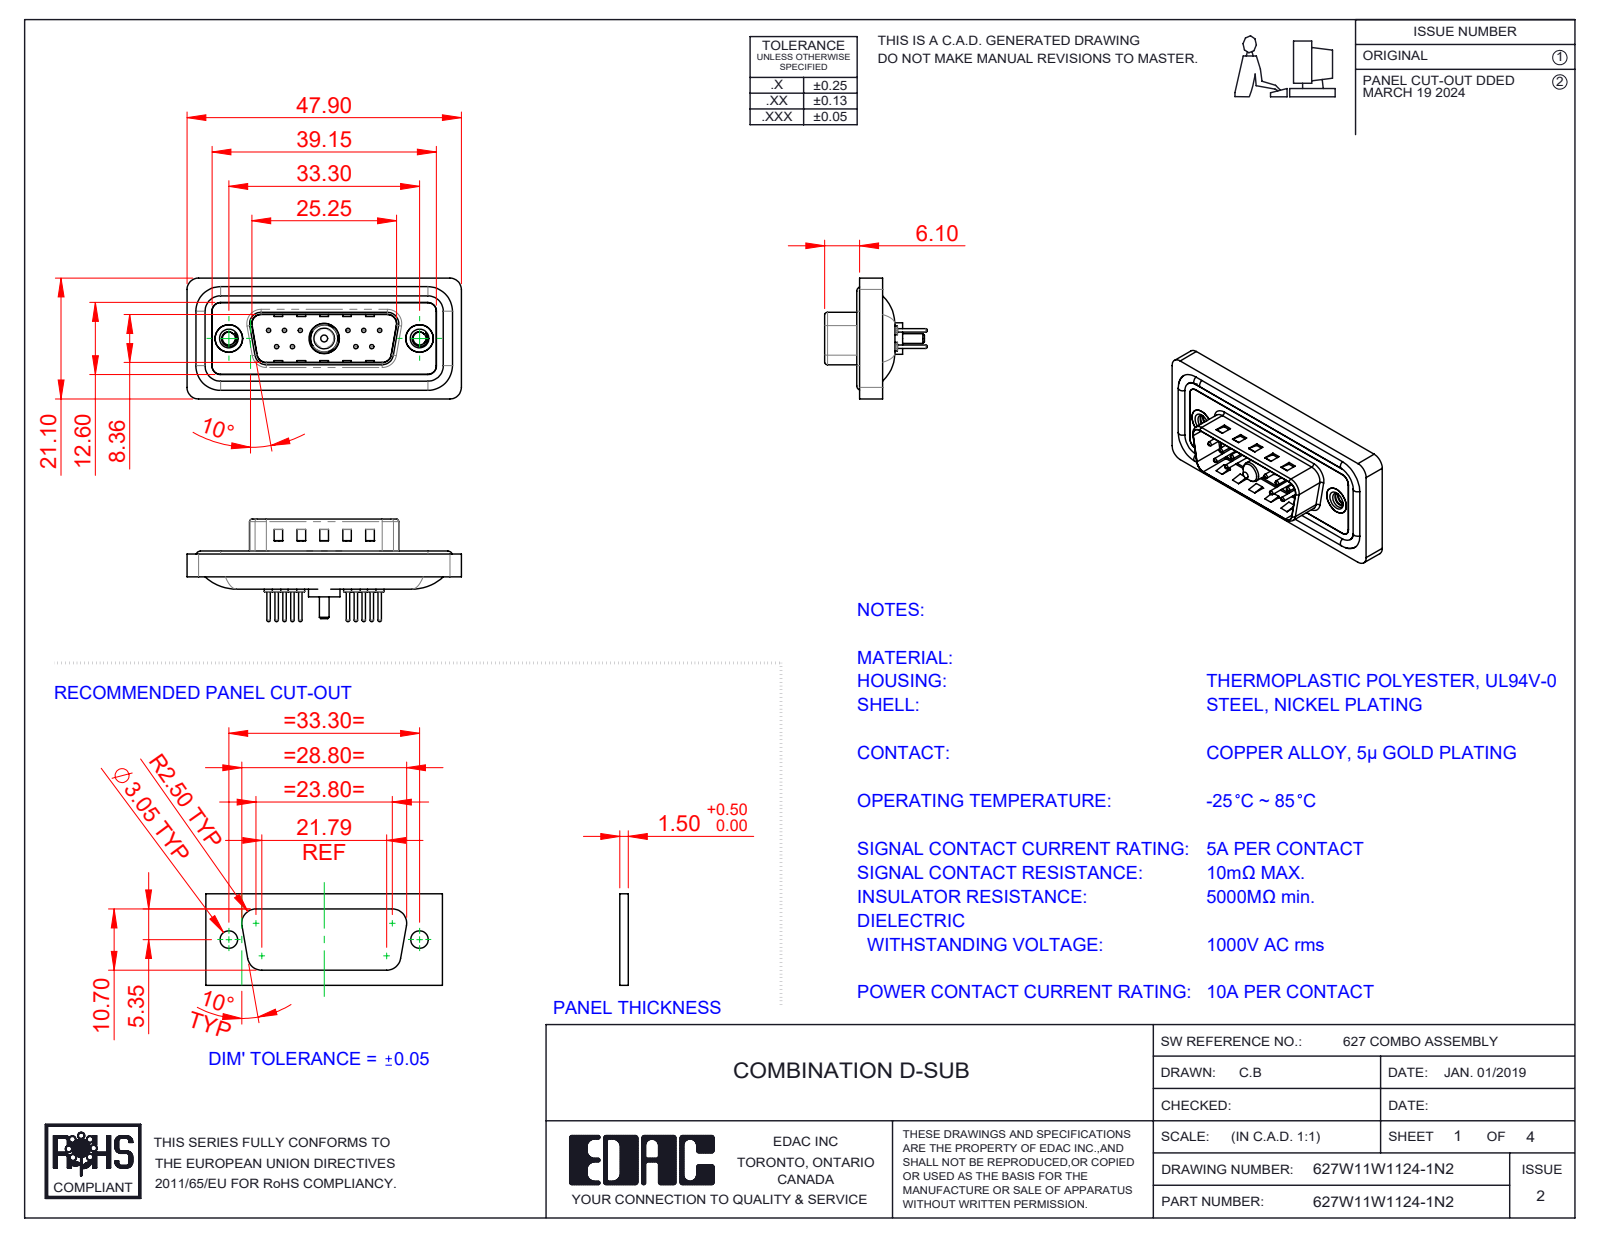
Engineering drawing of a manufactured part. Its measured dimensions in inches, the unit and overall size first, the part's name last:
Units: inches
Overall size (bounding box): 1.886 × 0.831 × 0.705
Round holes (diameter × count): ⌀0.03 ×10, ⌀0.063 ×10, ⌀0.079 ×10, ⌀0.089 ×2, ⌀0.157 ×2, ⌀0.189 ×2, ⌀0.197 ×2, ⌀0.191 ×1, ⌀0.209 ×1
Round bosses / shafts (diameter × count): ⌀0.059 ×10, ⌀0.024 ×10, ⌀0.063 ×4, ⌀0.193 ×2, ⌀0.217 ×1, ⌀0.205 ×1, ⌀0.187 ×1, ⌀0.148 ×1
Partial cylindrical surfaces — rounded edges, fillets, slot ends (radius × count): R0.059 ×26, R0.079 ×20, R0.02 ×8, R0.063 ×8, R0.039 ×7, R0.01 ×4, R0.024 ×4, R0.026 ×4
Main face-to-face distances: 0.016, 0.043, 0.063, 0.059, 0.122, 0.02, 0.114, 0.098, 0.161, 0.032
Hole centre spacings: 0.124, 0.109, 0.545, 0.436, 0.654, 0.198, 0.198, 0.218
Volume: 0.332 in³ · Surface area: 13.68 in²
Bodies: 19 solids, 869 faces (266 planar, 347 cylindrical, 256 other)
Part name (STEP PRODUCT): 627Combo Contact Row 1_24; 627Combo Housing_11W1; 627Combo Shell Rear_15 Contacts; 627Combo Threaded Rivet_2 (+5 more)
STEP written by: SolidWorks 2020 (CONFIG_CONTROL_DESIGN)
